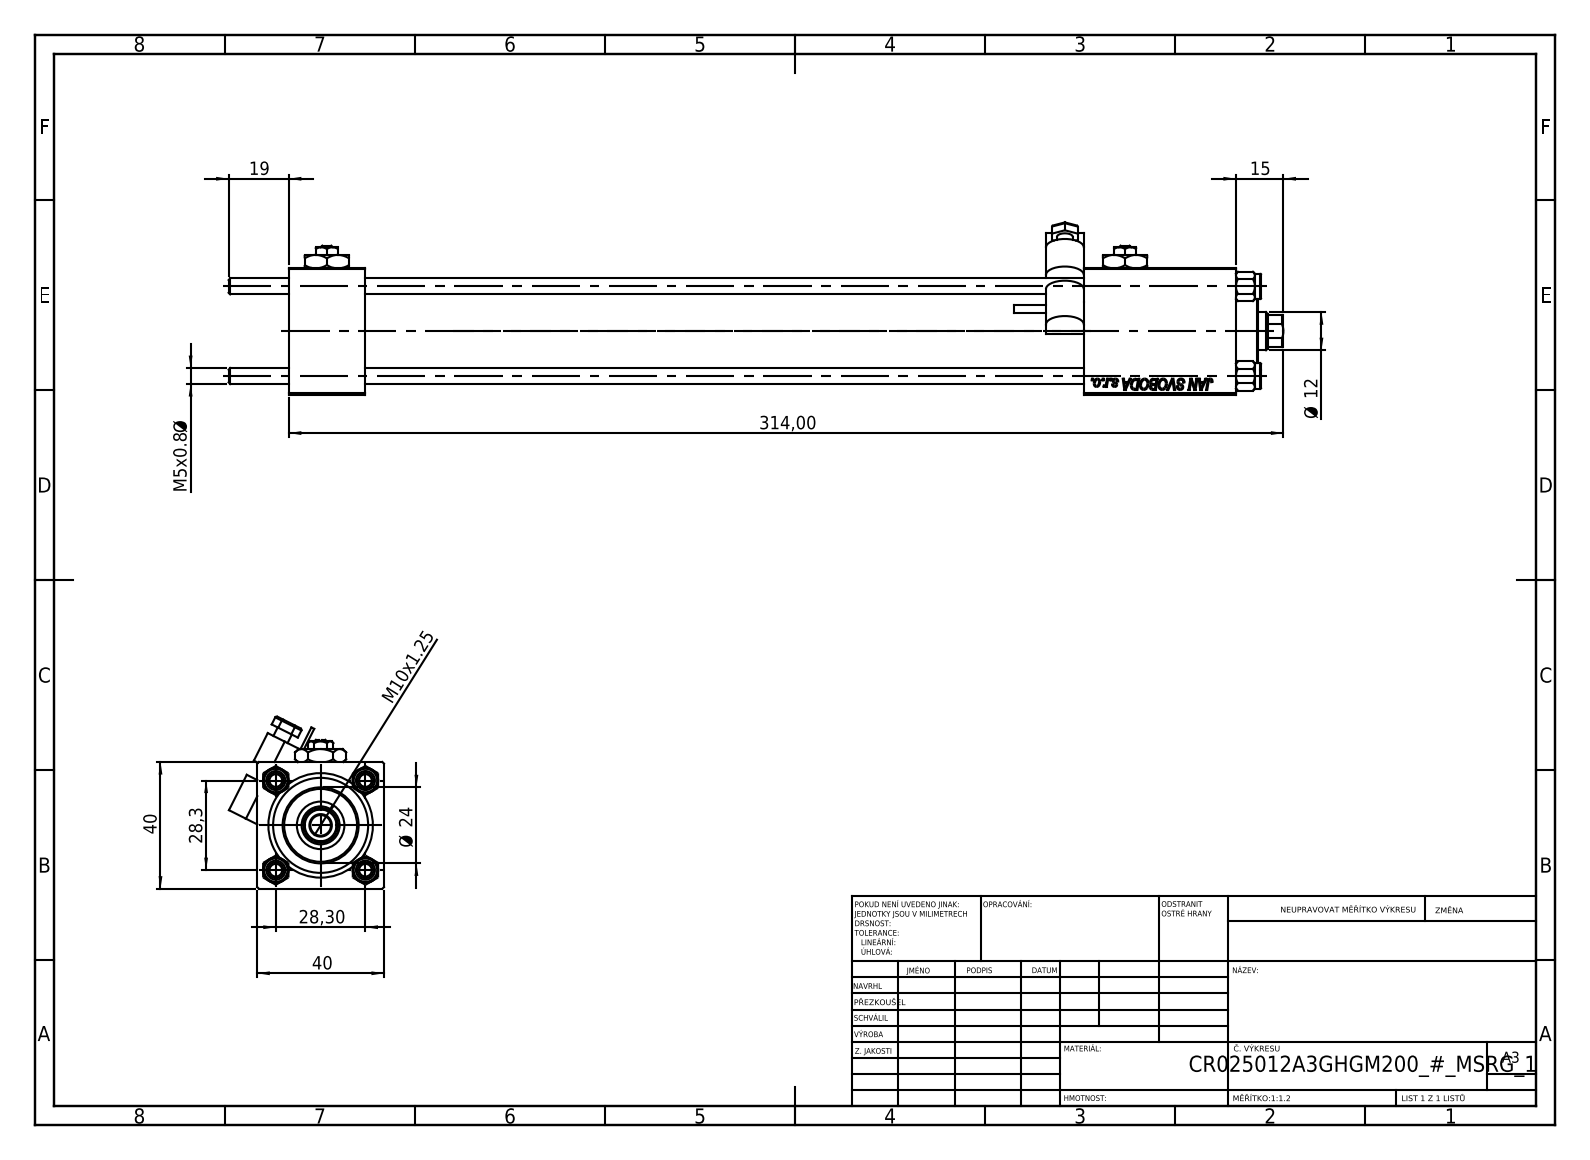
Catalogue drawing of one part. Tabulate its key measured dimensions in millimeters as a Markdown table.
| quantity | value |
| --- | --- |
| part name | NUT_M5; V215_VC_A; V215CR_BODY_A; V215CR_VCP (+3 more) |
| STEP written by | SolidWorks 2019 (CONFIG_CONTROL_DESIGN) |
| units | millimeters |
| bodies | 14 solids, 1264 faces (582 planar, 104 cylindrical, 578 other) |
| overall size | 333 × 54.35 × 48.93 |
| volume | 228 867 mm³ |
| surface area | 112 477 mm² |
| round holes (diameter × count) | 5 × 4, 20 × 3, 7 × 2, 13.16 × 2, 6.5 × 1, 12 × 1, 15 × 1, 25 × 1, 30 × 1 |
| round bosses / shafts (diameter × count) | 8 × 4, 31 × 1, 24 × 1, 5 × 1, 2.5 × 1 |
| partial cylindrical surfaces (radius × count) | 0.5 × 6, 6 × 2, 5.5 × 1 |
| main face-to-face distances | 40, 24, 251, 227, 39.8, 299, 275, 48, 270.3, 246.3 |
| hole center spacings | 20.01, 28.3, 40.02, 252 |
